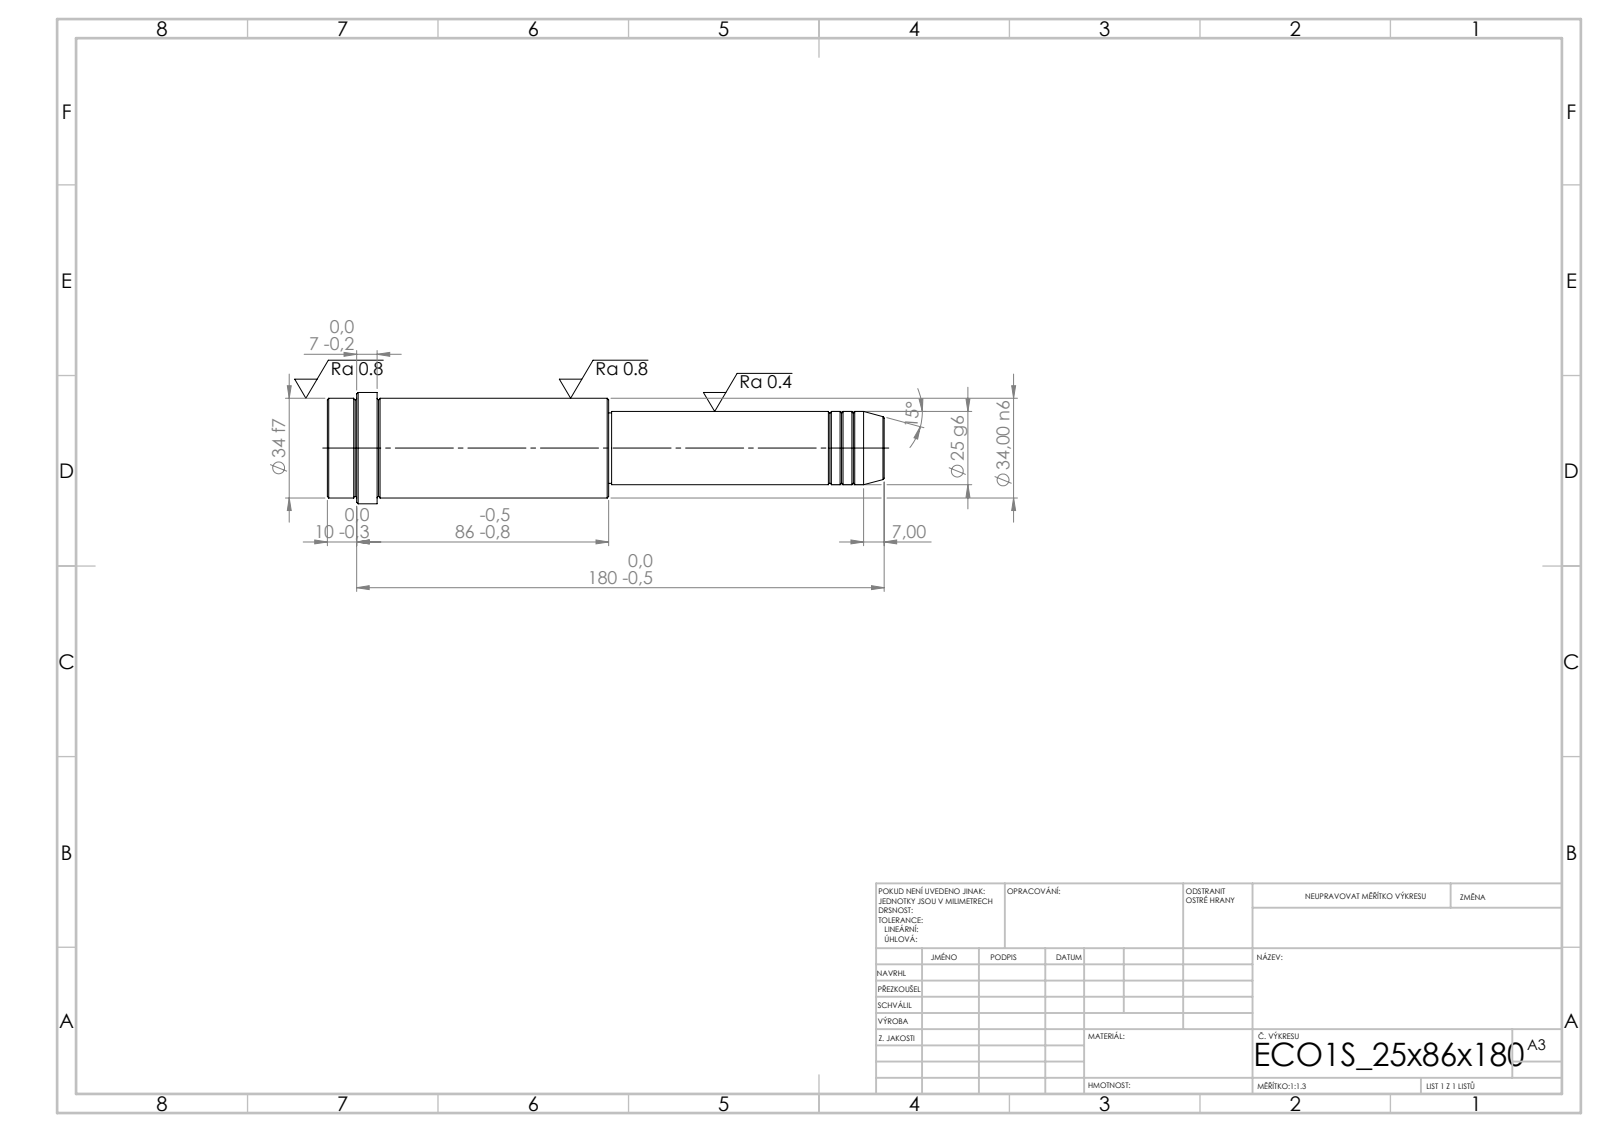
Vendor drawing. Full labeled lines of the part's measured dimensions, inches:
STEP written by: SolidWorks 2019 (CONFIG_CONTROL_DESIGN)
Units: inches
Bodies: 1 solid, 52 faces (6 planar, 16 cylindrical, 30 other)
Overall size (bounding box): 7.48 × 1.496 × 1.496
Volume: 8.186 in³ · Surface area: 31.07 in²
Round bosses / shafts (diameter × count): ⌀1.496 ×1, ⌀1.339 ×1, ⌀0.984 ×1, ⌀0.945 ×1
Main face-to-face distances: 3.78, 3.701, 7.48, 6.811, 3.11, 0.669, 7.087, 3.386, 0.276, 0.394
